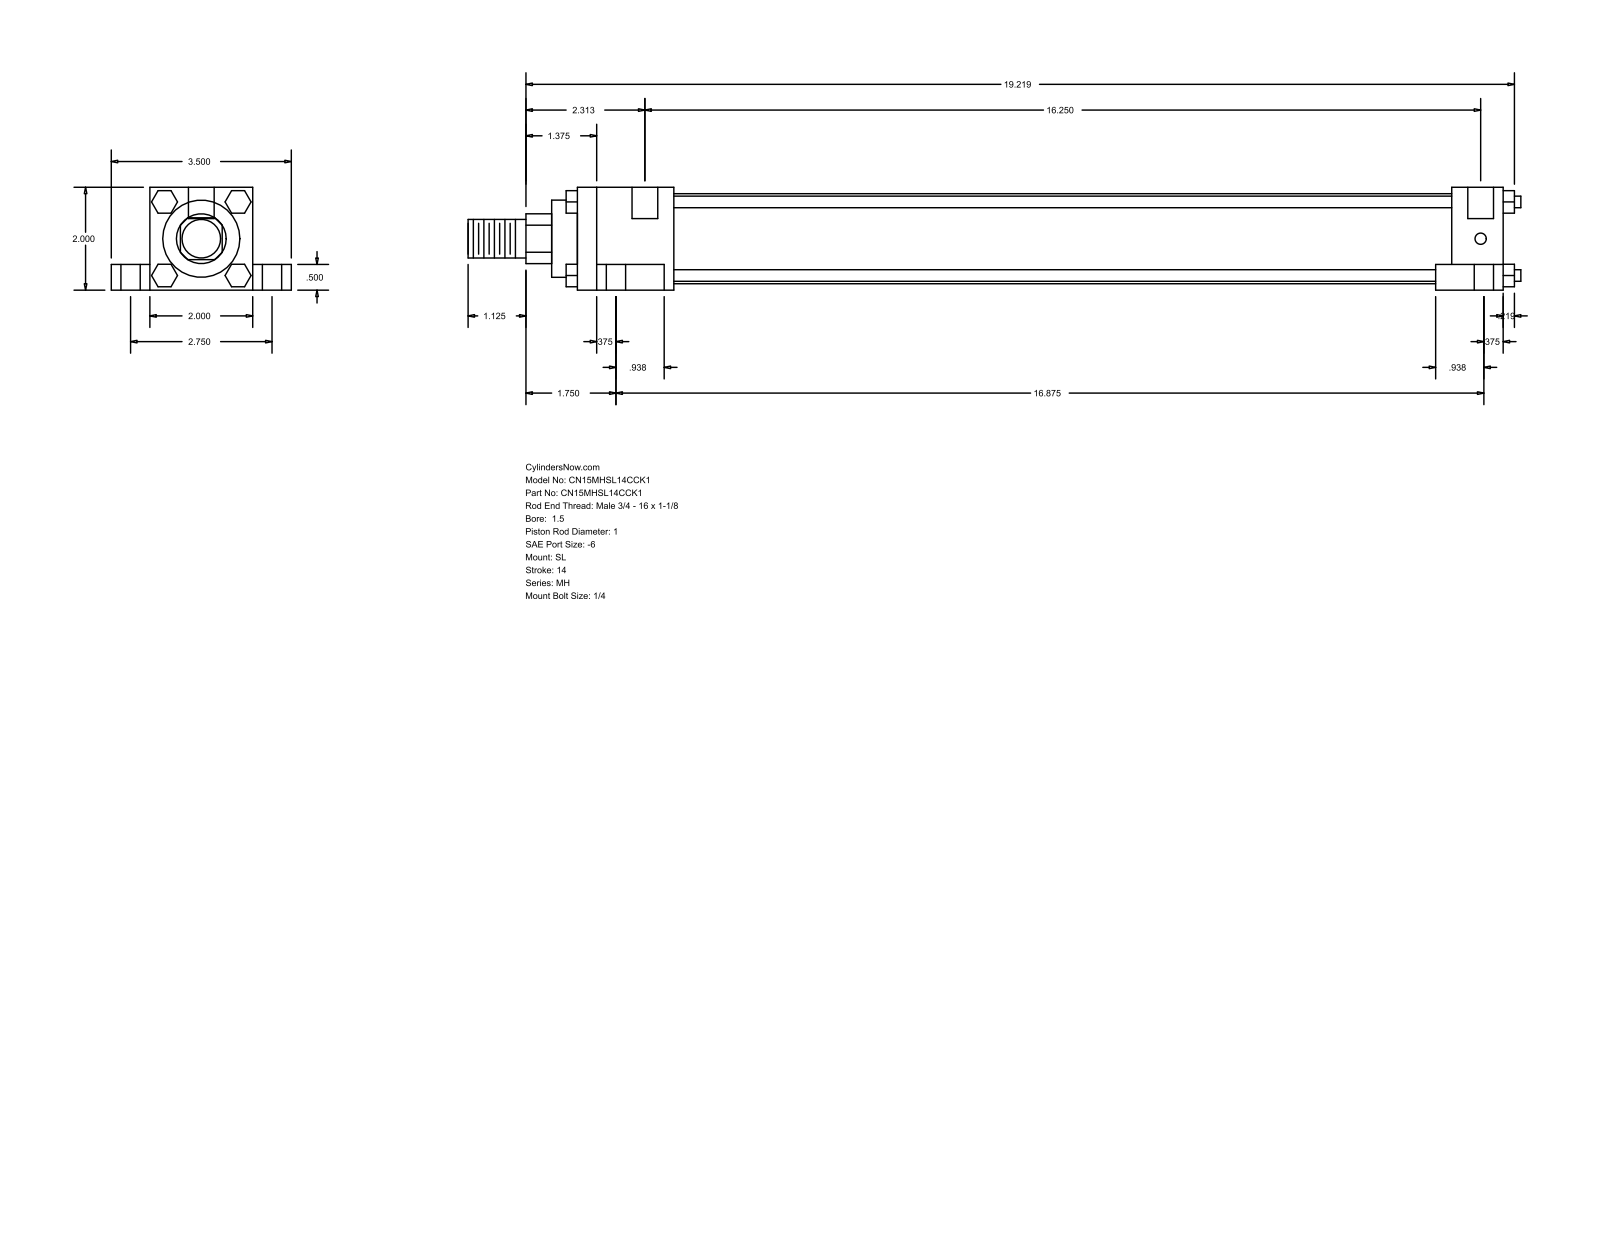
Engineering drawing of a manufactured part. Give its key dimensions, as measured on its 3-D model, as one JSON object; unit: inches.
{"part_name": "MH_SL__0150_1", "step_written_by": "GSSL Pune (CONFIG_CONTROL_DESIGN)", "units": "inches", "bodies": {"solids": 0, "faces": 148, "planar": 112, "cylindrical": 36, "other": 0}, "overall_size": [20.469, 3.5, 2], "round_holes": [[0.219, 4], [0.375, 4], [0.625, 4], [0.5, 2]], "round_bosses_or_shafts": [[0.225, 4], [1.75, 1], [1.5, 1], [1, 1], [0.75, 1]], "partial_cylinders_radius": [[0.484, 1]], "face_to_face_distances": [2, 0.5, 1.5, 0.75, 2.75, 18, 1, 0.375, 1.313, 16.313], "hole_center_spacings": [1.376, 1.443, 1.485, 2.75, 16.37, 16.375, 16.495, 16.869]}
